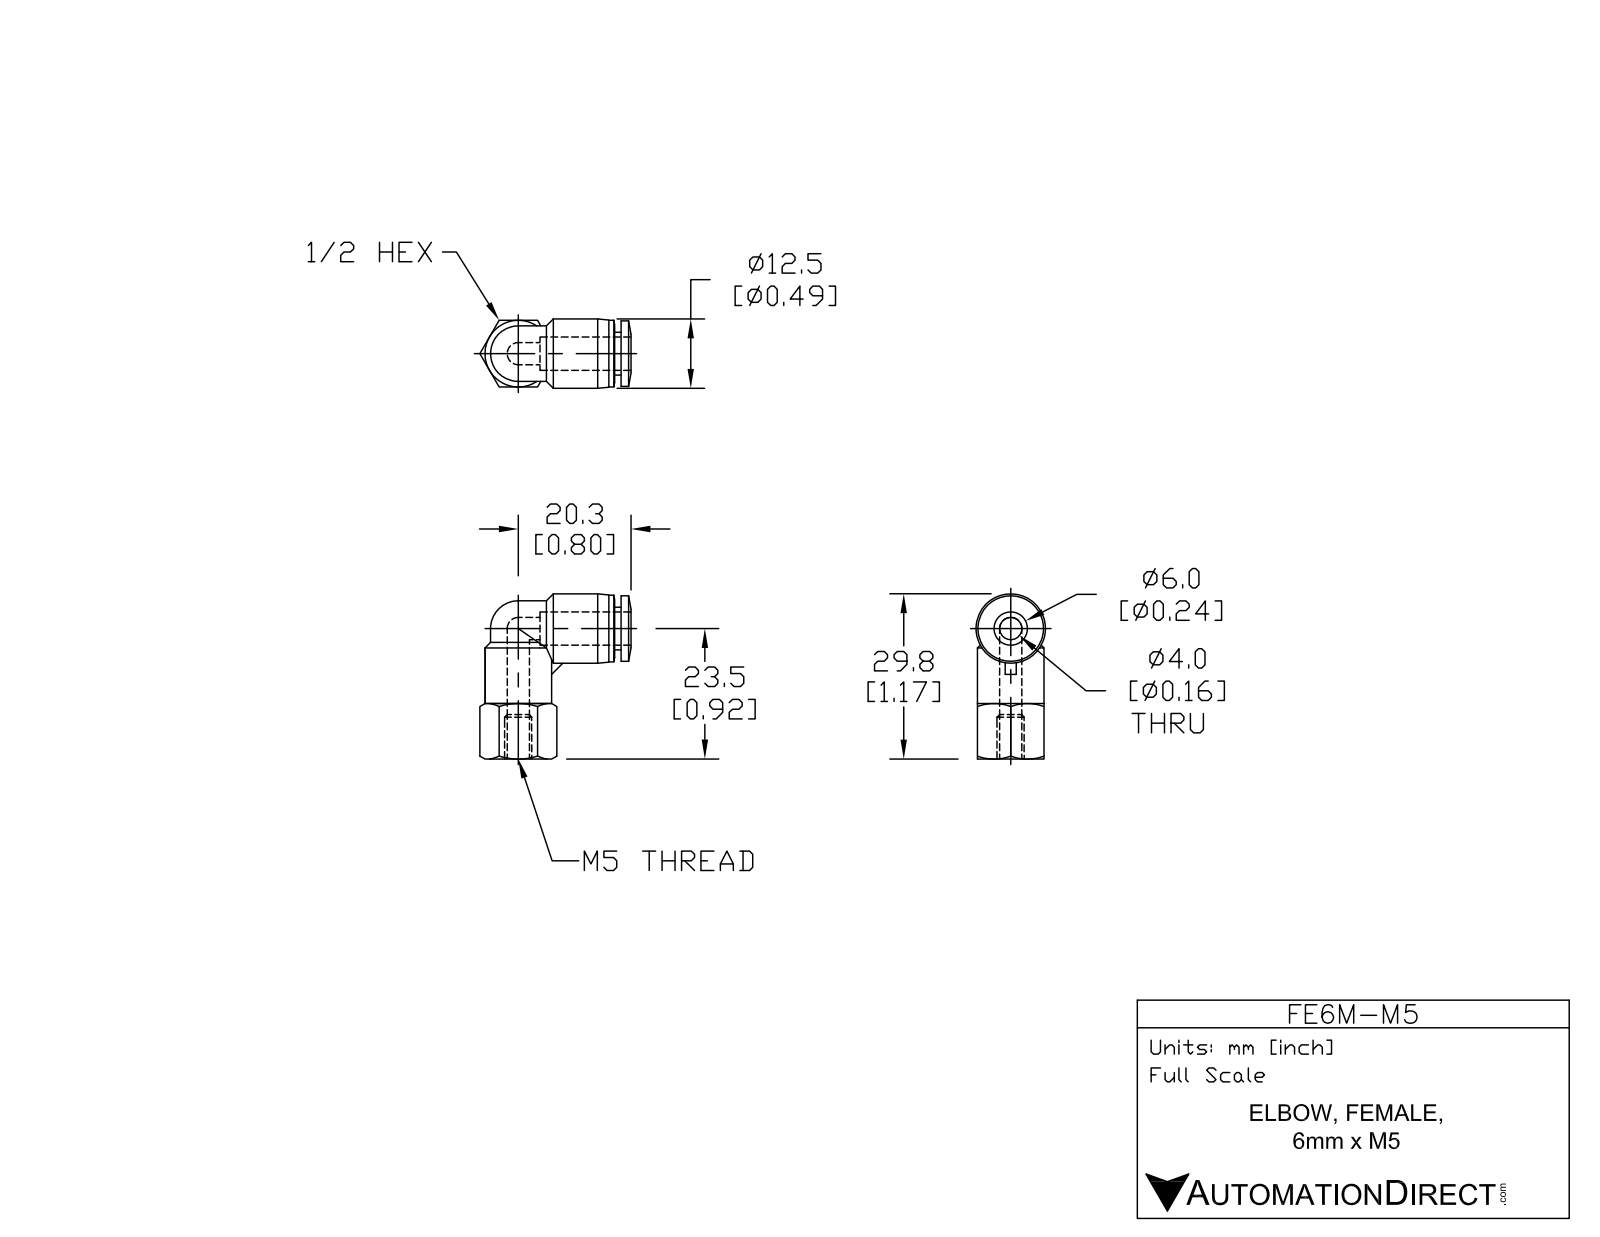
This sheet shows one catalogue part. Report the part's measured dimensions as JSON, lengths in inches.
{"part_name": "FE6M-M5", "step_written_by": "SolidWorks 2015 (AUTOMOTIVE_DESIGN)", "units": "inches", "bodies": {"solids": 1, "faces": 66, "planar": 16, "cylindrical": 21, "other": 29}, "overall_size": [1.171, 1.072, 0.492], "volume_in3": 0.231, "surface_area_in2": 4.101, "round_holes": [[0.165, 2], [0.197, 1], [0.248, 1]], "round_bosses_or_shafts": [[0.472, 2], [0.492, 1], [0.465, 1], [0.303, 1]], "partial_cylinders_radius": [[0.197, 2]], "face_to_face_distances": [0.472, 0.045, 0.53, 0.575, 0.315, 0.197, 0.276, 0.646, 0.116, 0.071]}
